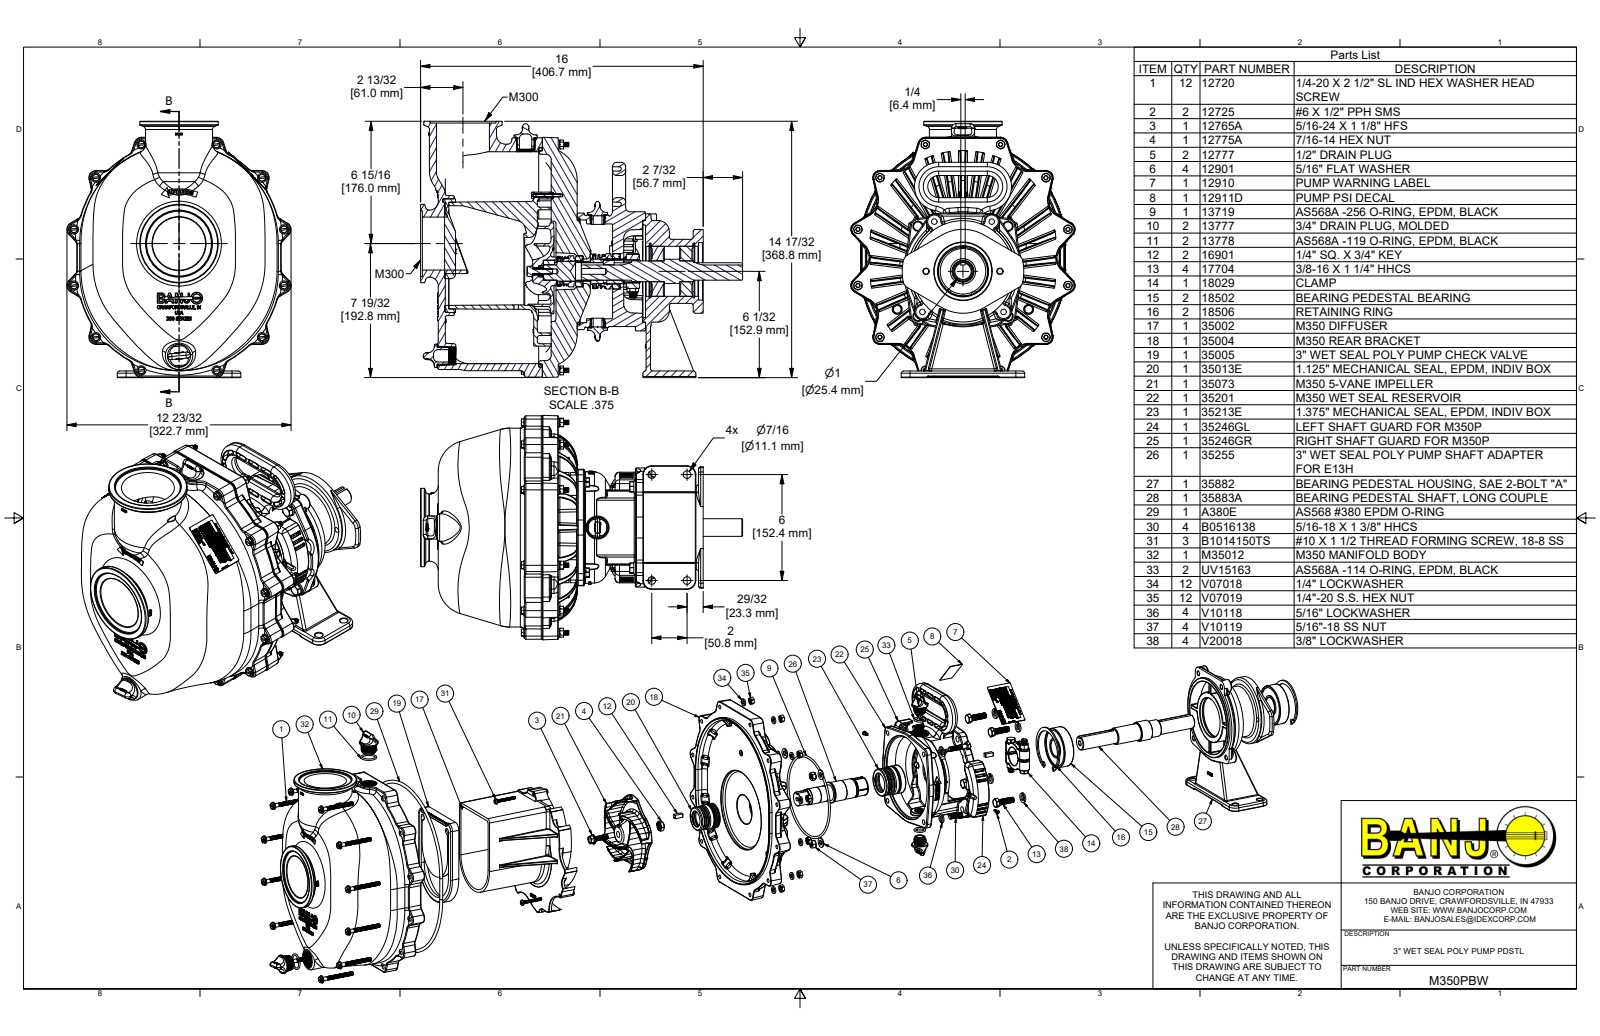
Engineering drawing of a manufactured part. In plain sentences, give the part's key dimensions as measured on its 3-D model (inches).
The part is named "M350PBW; 17704; 35073; 35002 (+8 more)". Its 3-D file was written by "Autodesk Inventor 2022 (AUTOMOTIVE_DESIGN)". It is 112 solids with 24601 faces: 8598 planar, 3829 cylindrical and 12174 other. Overall it measures 18.243 by 14.518 by 12.712 inches. Its volume is 400.6 cubic inches and its surface area 2 752 square inches. Round holes: 12 of diameter 0.196, 12 of diameter 0.252, 12 of diameter 0.27, 10 of diameter 0.52, 6 of diameter 0.307, 6 of diameter 0.385, 5 of diameter 0.437, 4 of diameter 0.252, 4 of diameter 0.313, 4 of diameter 0.322, 4 of diameter 0.344, 4 of diameter 0.344. Round bosses or shafts: 76 of diameter 0.324, 46 of diameter 0.337, 12 of diameter 0.489, 12 of diameter 0.25, 6 of diameter 0.687, 6 of diameter 0.375, 4 of diameter 0.688, 4 of diameter 0.583. Partial cylindrical surfaces (rounded edges, fillets, slot ends): 309 of radius 0.031, 195 of radius 0.062, 88 of radius 0.125, 75 of radius 0.016, 69 of radius 0.094, 54 of radius 0.03, 52 of radius 0.25, 46 of radius 0.375. The main face-to-face distances are 0.4, 6.4, 0.5, 0.9, 5.014, 4.05, 0.2, 5.5, 0.269, 6.669. The hole center spacings are 6.005, 3.182, 9.407, 3.611, 5.107, 6.137, 6.236, 6.408.
